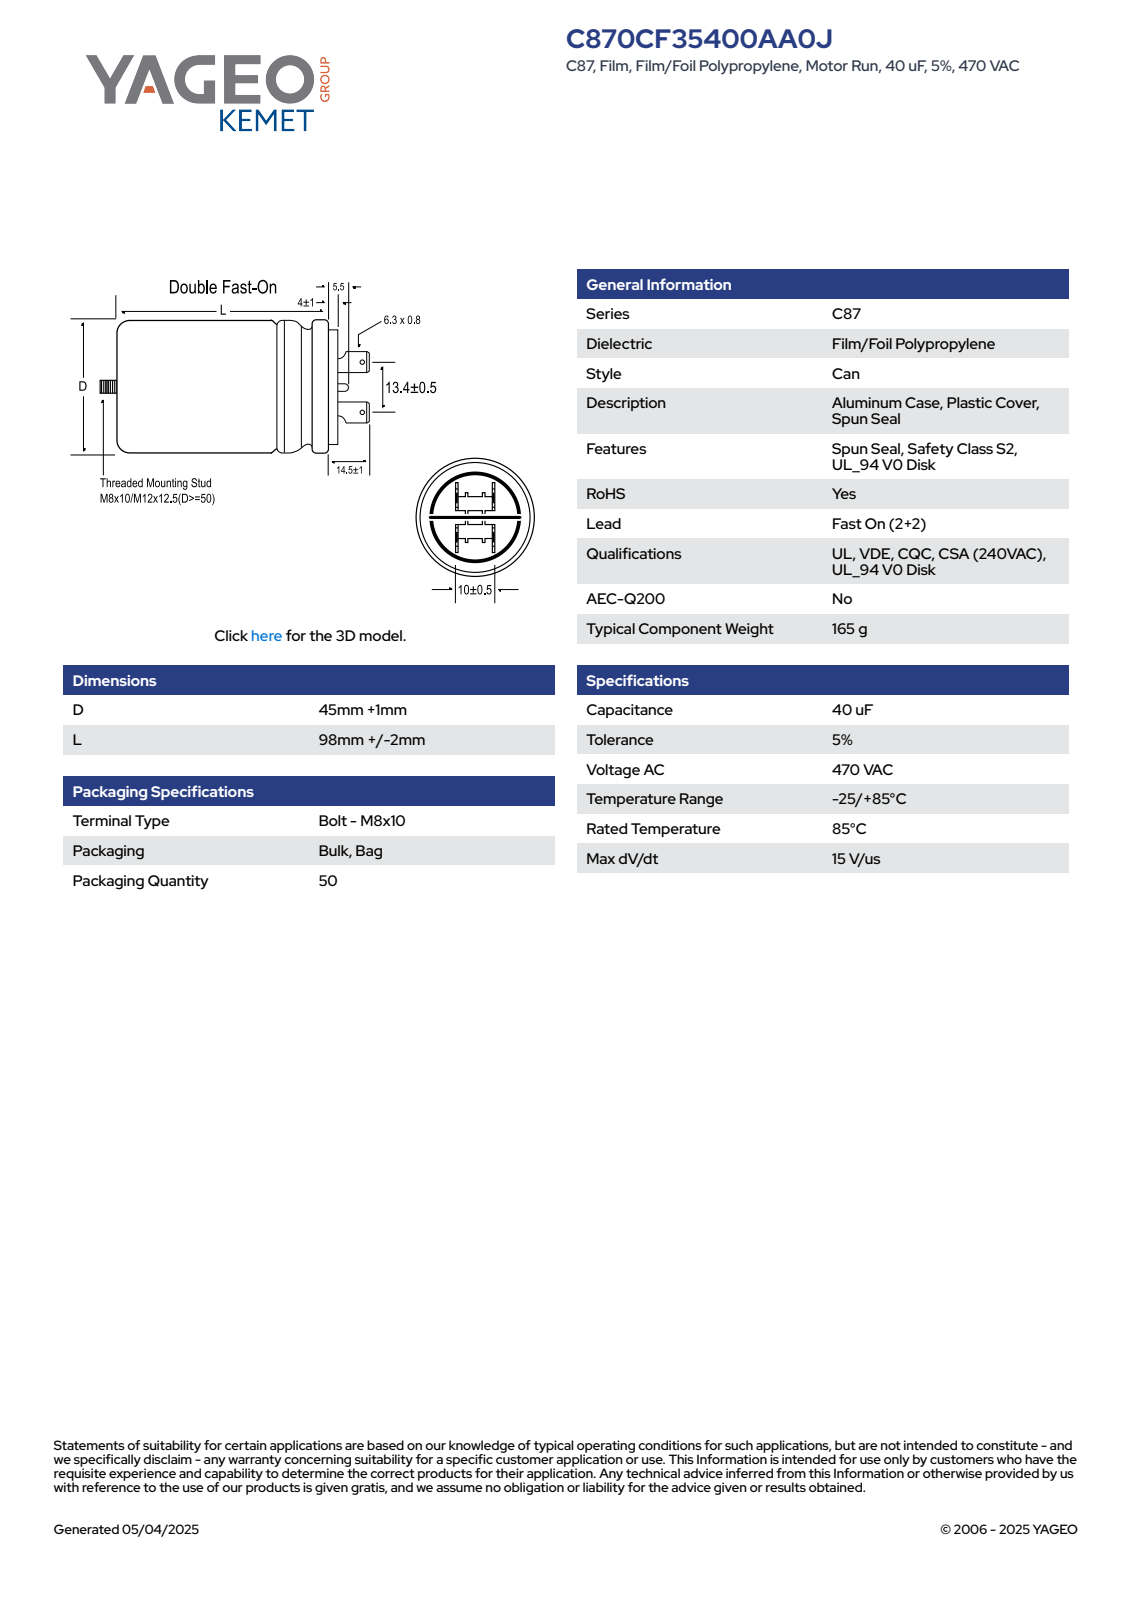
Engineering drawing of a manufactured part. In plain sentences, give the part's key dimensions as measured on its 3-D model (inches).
The part is named "CFM_C87DF_45X98_D46L100". Its 3-D file was written by "SolidWorks 2014 (AUTOMOTIVE_DESIGN)". It is 1 solid with 153 faces: 52 planar, 58 cylindrical and 43 other. Overall it measures 4.941 by 1.811 by 1.811 inches. Its volume is 10.29 cubic inches and its surface area 30.2 square inches. Round holes: 2 of diameter 0.047. Round bosses or shafts: 1 of diameter 1.811, 1 of diameter 1.546, 1 of diameter 0.315. Partial cylindrical surfaces (rounded edges, fillets, slot ends): 9 of radius 0.01, 2 of radius 0.157, 1 of radius 0.905. The main face-to-face distances are 4.134, 3.669, 0.465, 0.031, 0.382, 3.937, 0.268, 0.197, 0.413, 0.35. The hole center spacings are 0.547.
